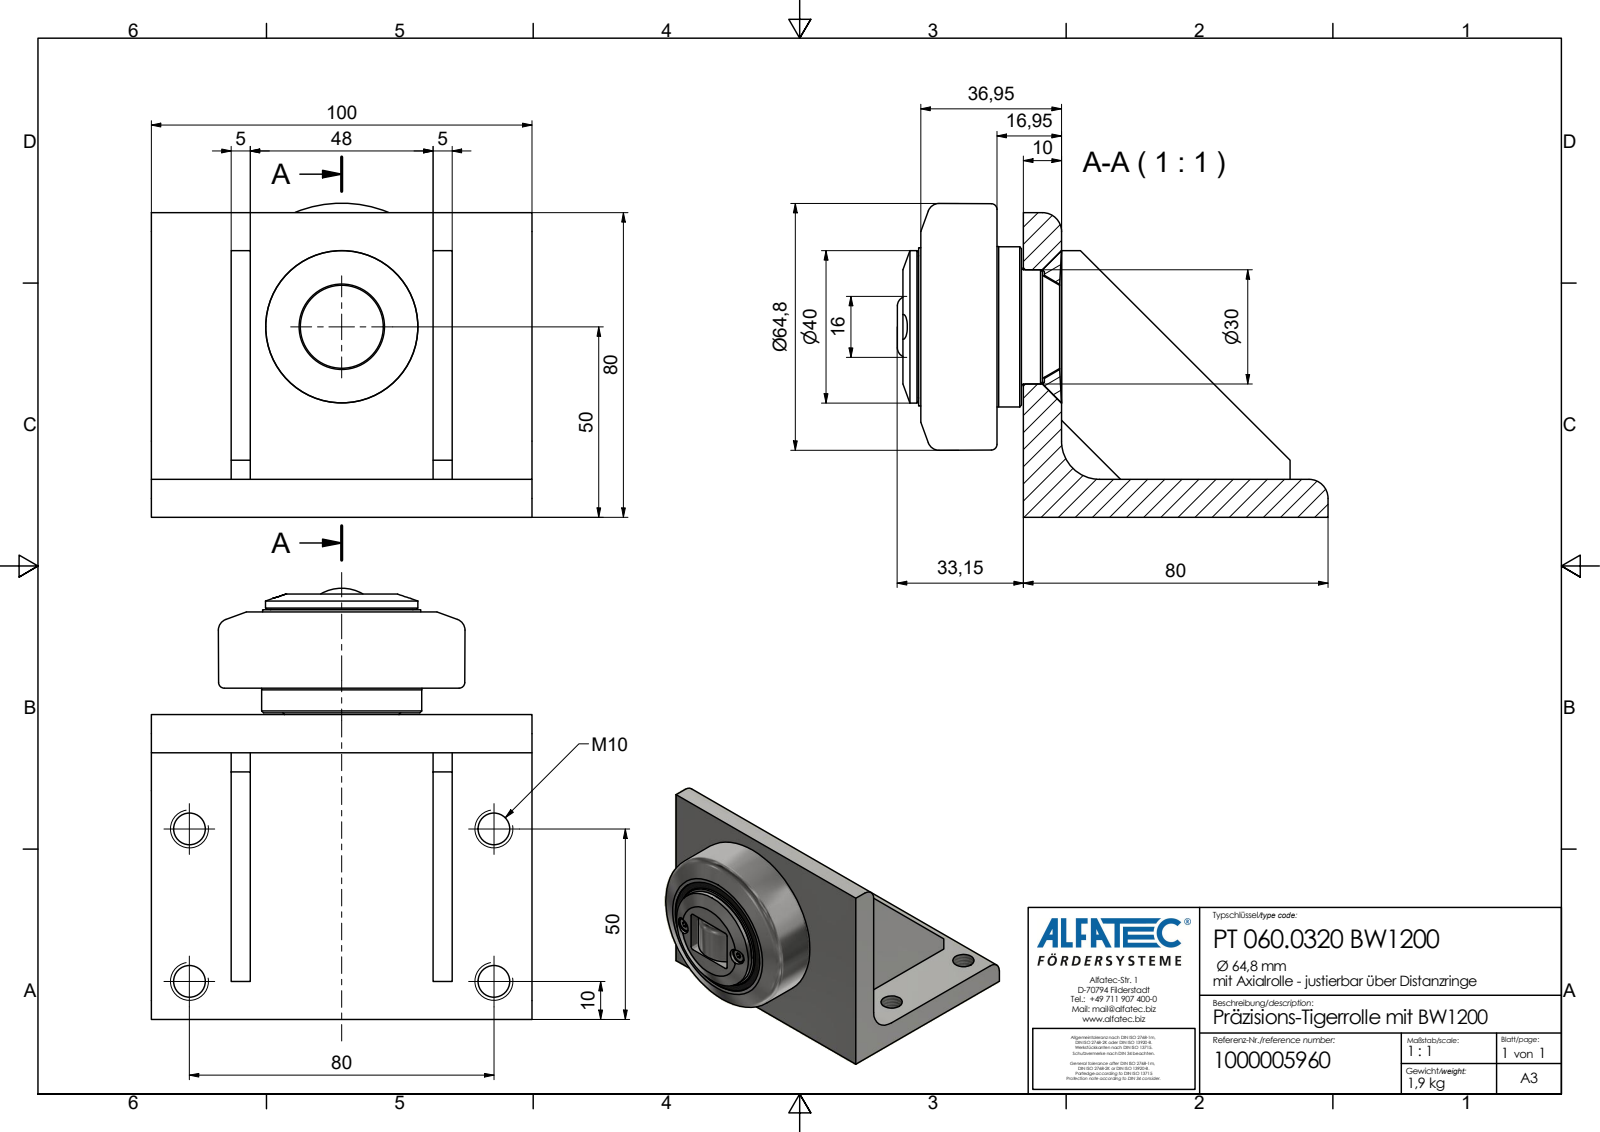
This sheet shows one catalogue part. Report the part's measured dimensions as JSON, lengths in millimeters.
{"part_name": "PT 060.0320 BW1200_Kontur", "step_written_by": "Autodesk Inventor 2020 (AP242_MANAGED_MODEL_BASED_3D_ENGINEERING_MIM_LF)", "units": "millimeters", "bodies": {"solids": 1, "faces": 136, "planar": 65, "cylindrical": 43, "other": 28}, "overall_size": [113.15, 100, 82.4], "volume_mm3": 243420, "surface_area_mm2": 58205, "round_holes": [[8.38, 4], [3.4, 2], [6.5, 2], [10.2, 1], [13, 1], [16, 1], [38, 1], [42, 1], [42.97, 1], [47, 1]], "round_bosses_or_shafts": [[5.35, 2], [3, 2], [42.1, 1], [41.5, 1], [40, 1], [25, 1], [11, 1]], "partial_cylinders_radius": [[1, 4], [5, 2], [10, 1], [12.47, 1]], "face_to_face_distances": [10, 5, 53, 21, 26, 74, 79, 58, 48, 6.95], "hole_center_spacings": [15, 30, 40, 65.72, 80, 89.44, 100.46]}
